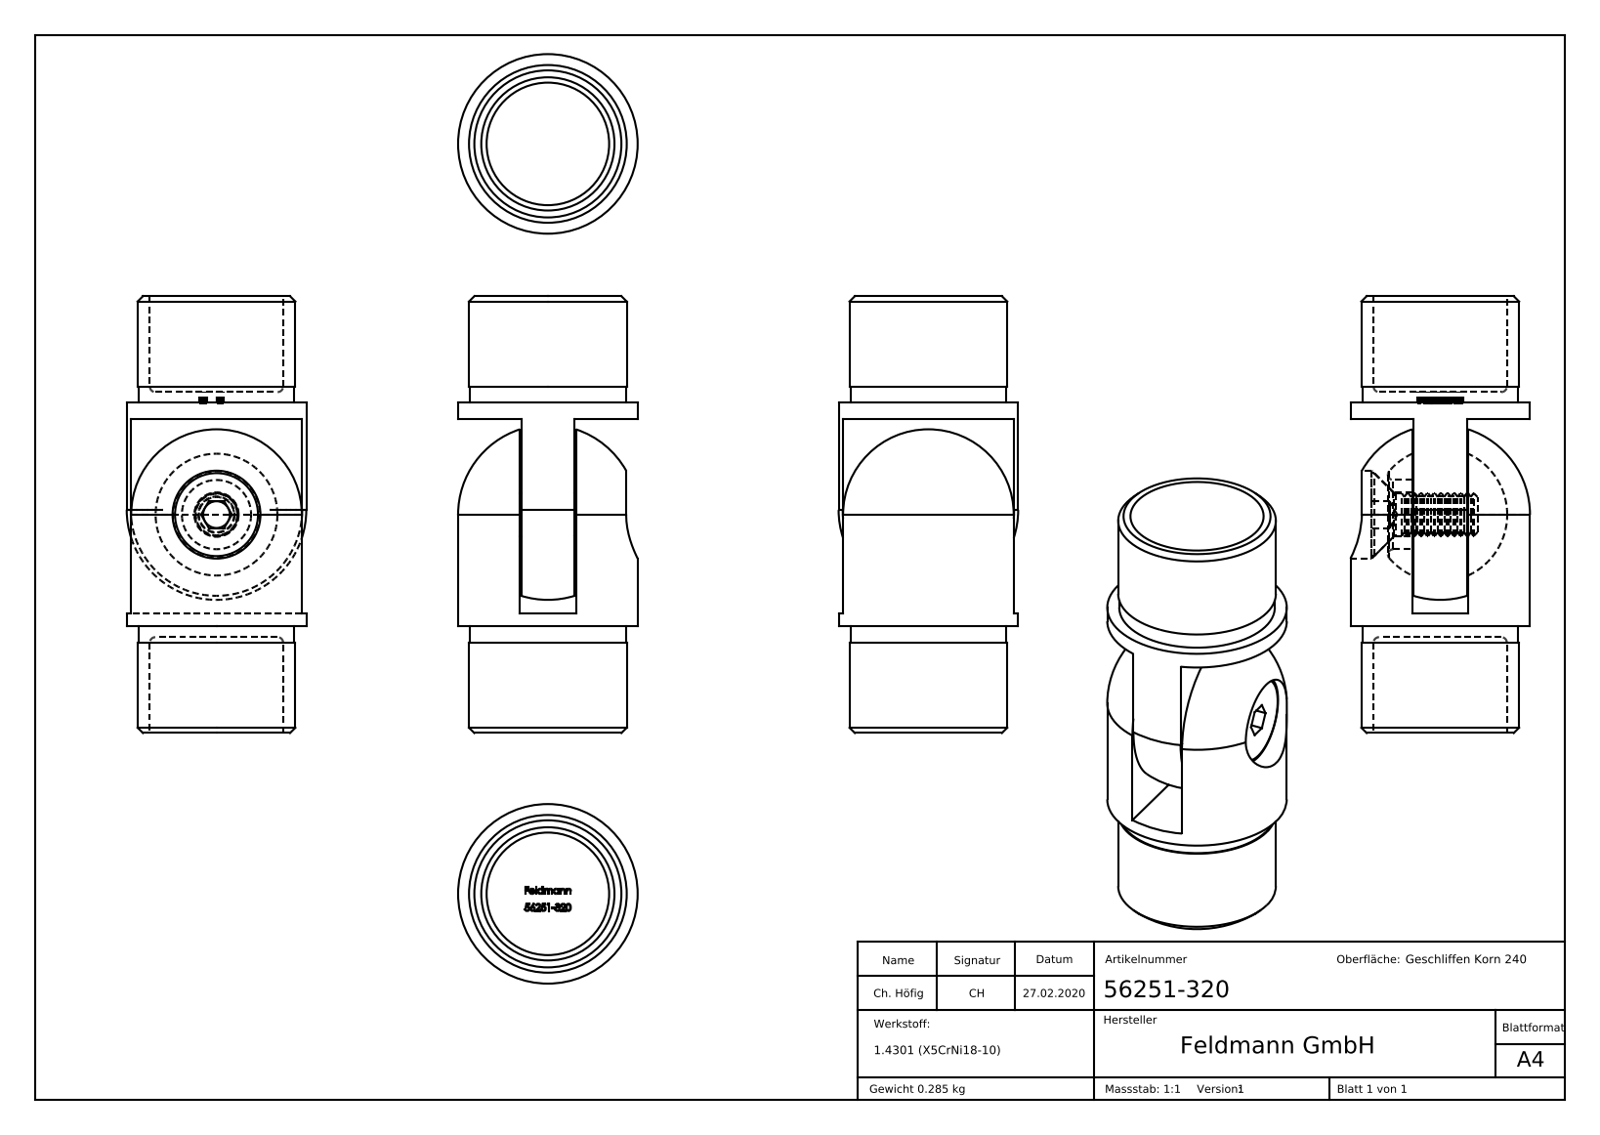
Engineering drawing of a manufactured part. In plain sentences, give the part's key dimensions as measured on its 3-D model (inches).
The part is named "56251-320; socket countersunk head screw_din_DIN 7991 - M8 x 20 --- 20S; 5625X-320 Teil1_56251-320 Teil1; 5625X-320 Teil2_56251-320 Teil2 (+3 more)". Its 3-D file was written by "SolidWorks 2015 (CONFIG_CONTROL_DESIGN)". It is 3 solids with 318 faces: 146 planar, 25 cylindrical and 147 other. Overall it measures 3.228 by 1.327 by 1.327 inches. Its volume is 2.259 cubic inches and its surface area 29.96 square inches. Round holes: 1 of diameter 0.268, 1 of diameter 0.323, 1 of diameter 0.65, 1 of diameter 0.984. Round bosses or shafts: 1 of diameter 1.327, 1 of diameter 1.165, 1 of diameter 1.15, 1 of diameter 0.613, 1 of diameter 0.512, 1 of diameter 0.315. The main face-to-face distances are 0.404, 0.394, 0.413, 0.079, 1.732, 1.614, 1.811, 0.197, 0.709, 0.177.
